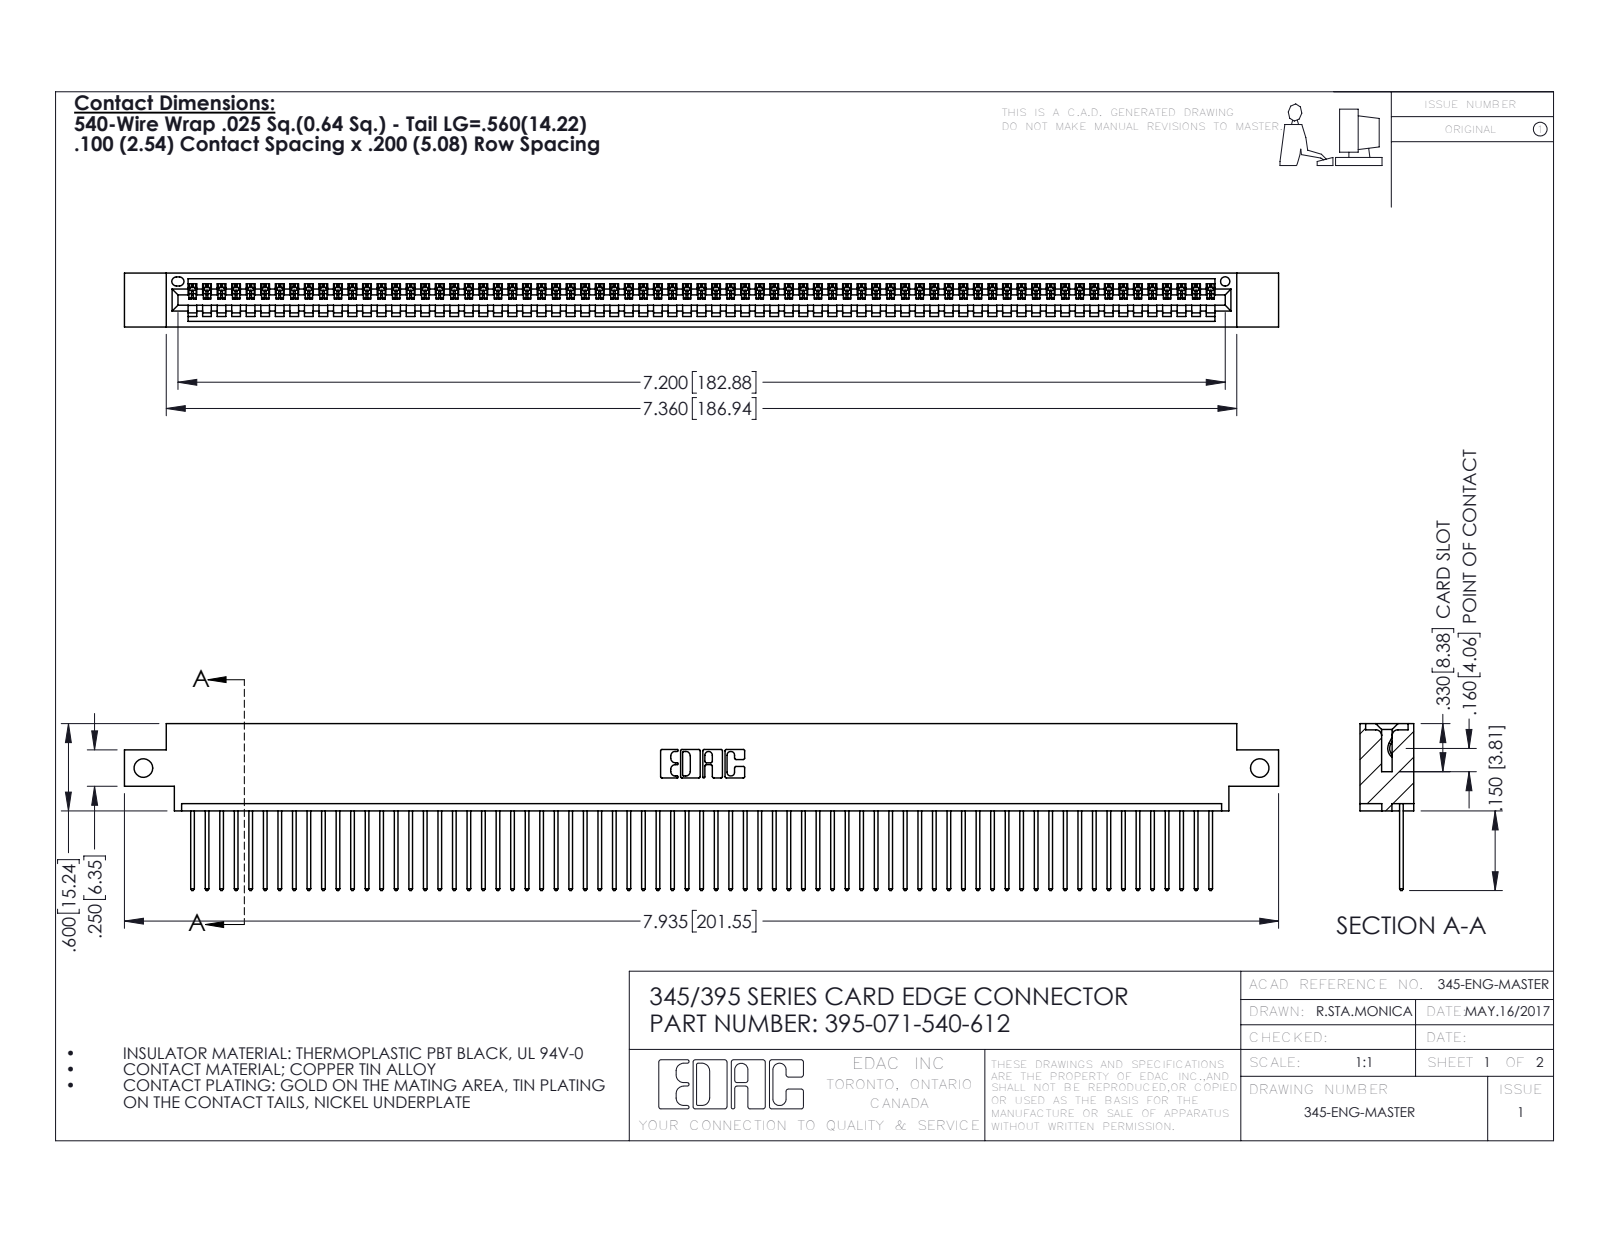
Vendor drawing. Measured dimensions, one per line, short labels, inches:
name: 395-071-540-612; 345-292-001_345-293-140; 345 Part_0.170 Offset - Side Mount
written by: SolidWorks 2016 (CONFIG_CONTROL_DESIGN)
unit: in
bodies: 72 solids, 4248 faces (2924 planar, 1324 cylindrical, 0 other)
size: 7.935 × 1.147 × 0.37
volume: 1.176 in³; area: 41.37 in²
holes: 2× ⌀0.128, 1× ⌀0.064
rounds: 142× R0.006, 142× R0.01, 22× R0.01, 6× R0.007, 6× R0.031, 3× R0.026, 2× R0.031, 2× R0.04
face distances: 0.072, 0.298, 0.37, 0.098, 0.272, 0.025, 0.2, 0.225, 0.175, 0.149
hole spacings: 7.675
